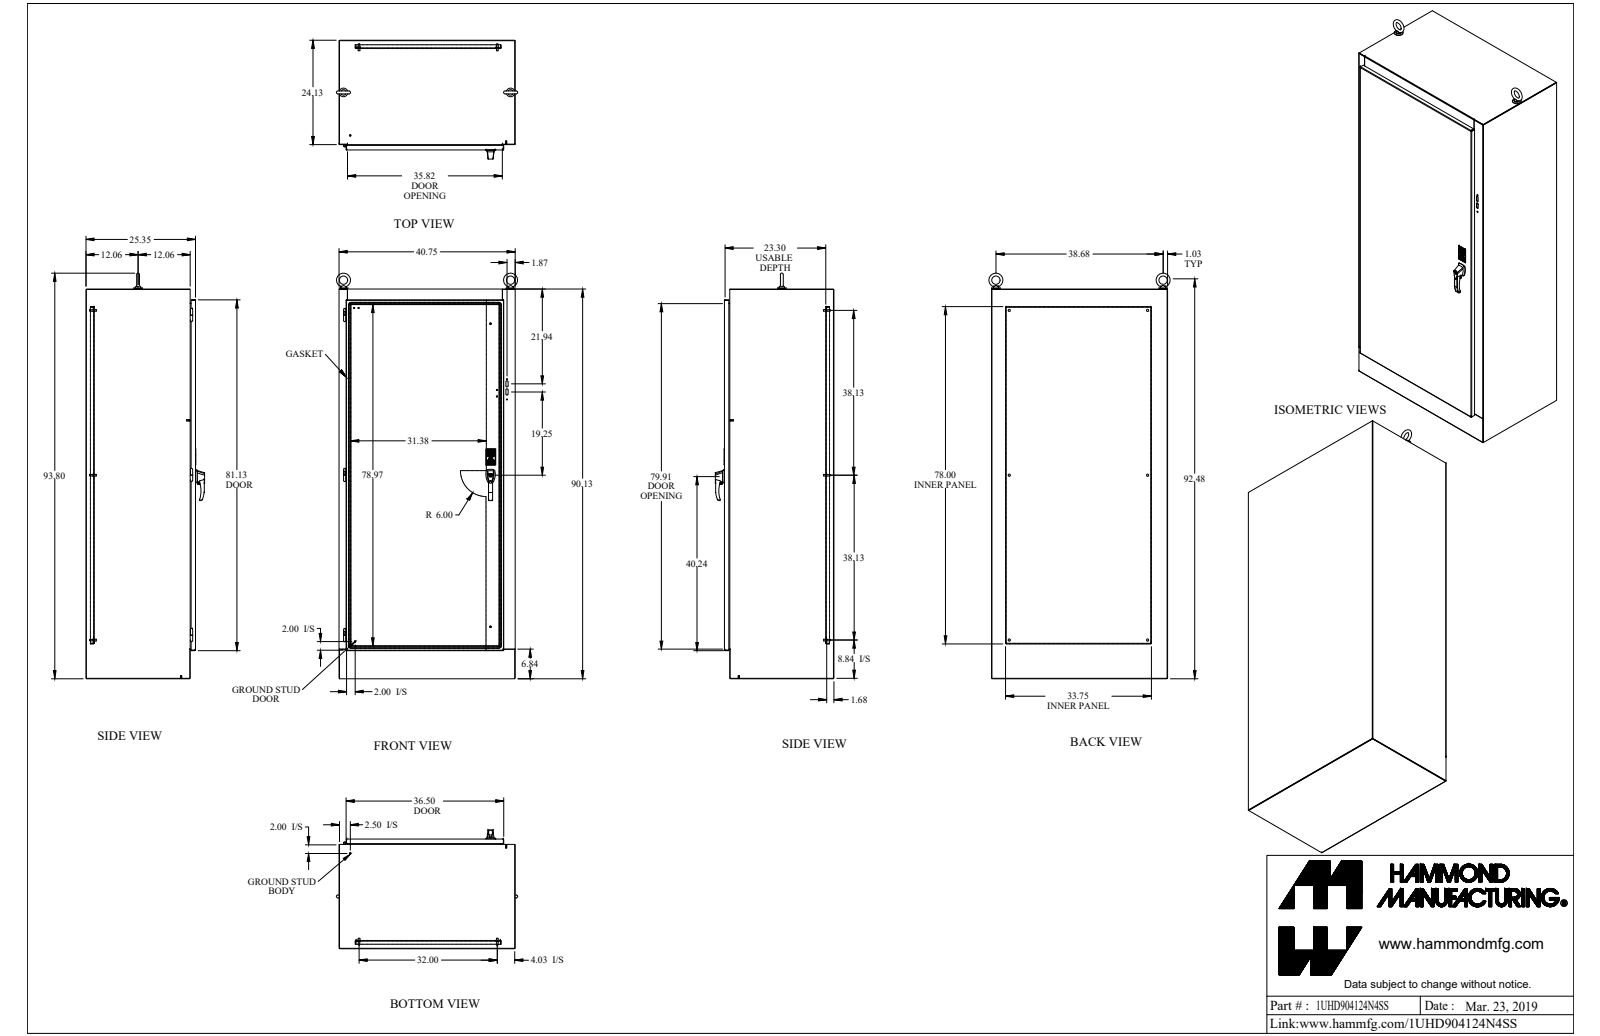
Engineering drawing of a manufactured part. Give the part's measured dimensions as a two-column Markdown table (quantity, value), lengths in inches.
| quantity | value |
| --- | --- |
| part name | 1UHD904124N4SS |
| STEP written by | SolidWorks 2018 (AUTOMOTIVE_DESIGN) |
| units | inches |
| bodies | 112 solids, 2003 faces (1132 planar, 535 cylindrical, 336 other) |
| overall size | 93.799 × 41.932 × 27.464 |
| volume | 1 881 in³ |
| surface area | 37 646 in² |
| round holes (diameter × count) | 0.35 × 7, 0.196 × 6, 0.307 × 6, 0.563 × 6, 0.25 × 5, 0.156 × 4, 0.281 × 4, 0.445 × 4, 0.313 × 3, 0.167 × 2, 0.189 × 2, 0.255 × 2 |
| round bosses / shafts (diameter × count) | 0.25 × 11, 1 × 8, 0.375 × 7, 0.65 × 6, 0.332 × 6, 0.19 × 4, 0.625 × 3, 0.5 × 3 |
| partial cylindrical surfaces (radius × count) | 0.125 × 27, 0.048 × 24, 0.143 × 24, 0.5 × 23, 0.06 × 19, 0.25 × 19, 0.017 × 16, 0.032 × 12 |
| main face-to-face distances | 0.095, 25.254, 40.655, 25.159, 25.349, 0.125, 1.907, 1.812, 23.348, 23.443 |
| hole center spacings | 32, 7.5, 9.22, 12.875, 14.9, 30.461, 33.937, 36.188 |
